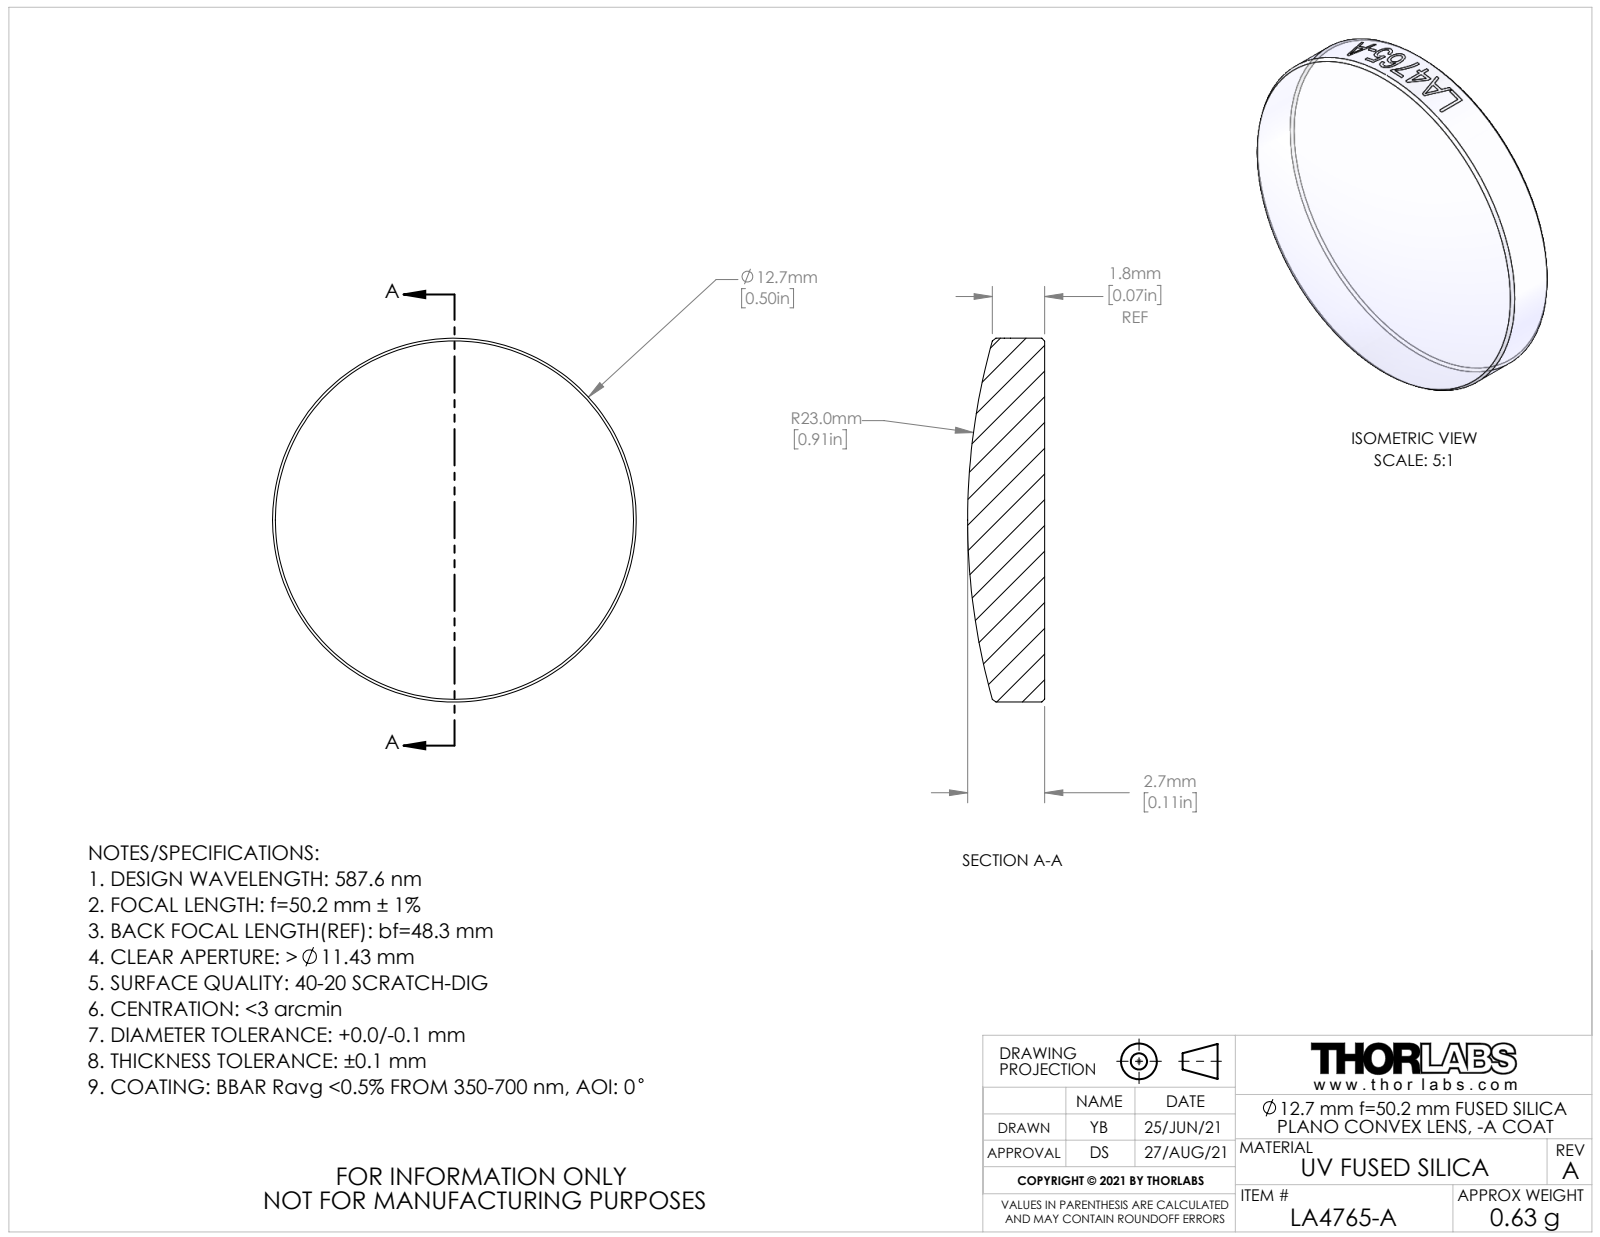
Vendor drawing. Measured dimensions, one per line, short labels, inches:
name: CTN017528-E0W; CTN017556
written by: SolidWorks 2018 (AUTOMOTIVE_DESIGN)
unit: in
bodies: 1 solid, 21 faces (1 planar, 14 cylindrical, 6 other)
size: 0.5 × 0.5 × 0.106
volume: 0.017 in³; area: 0.502 in²
bosses: 1× ⌀0.5
